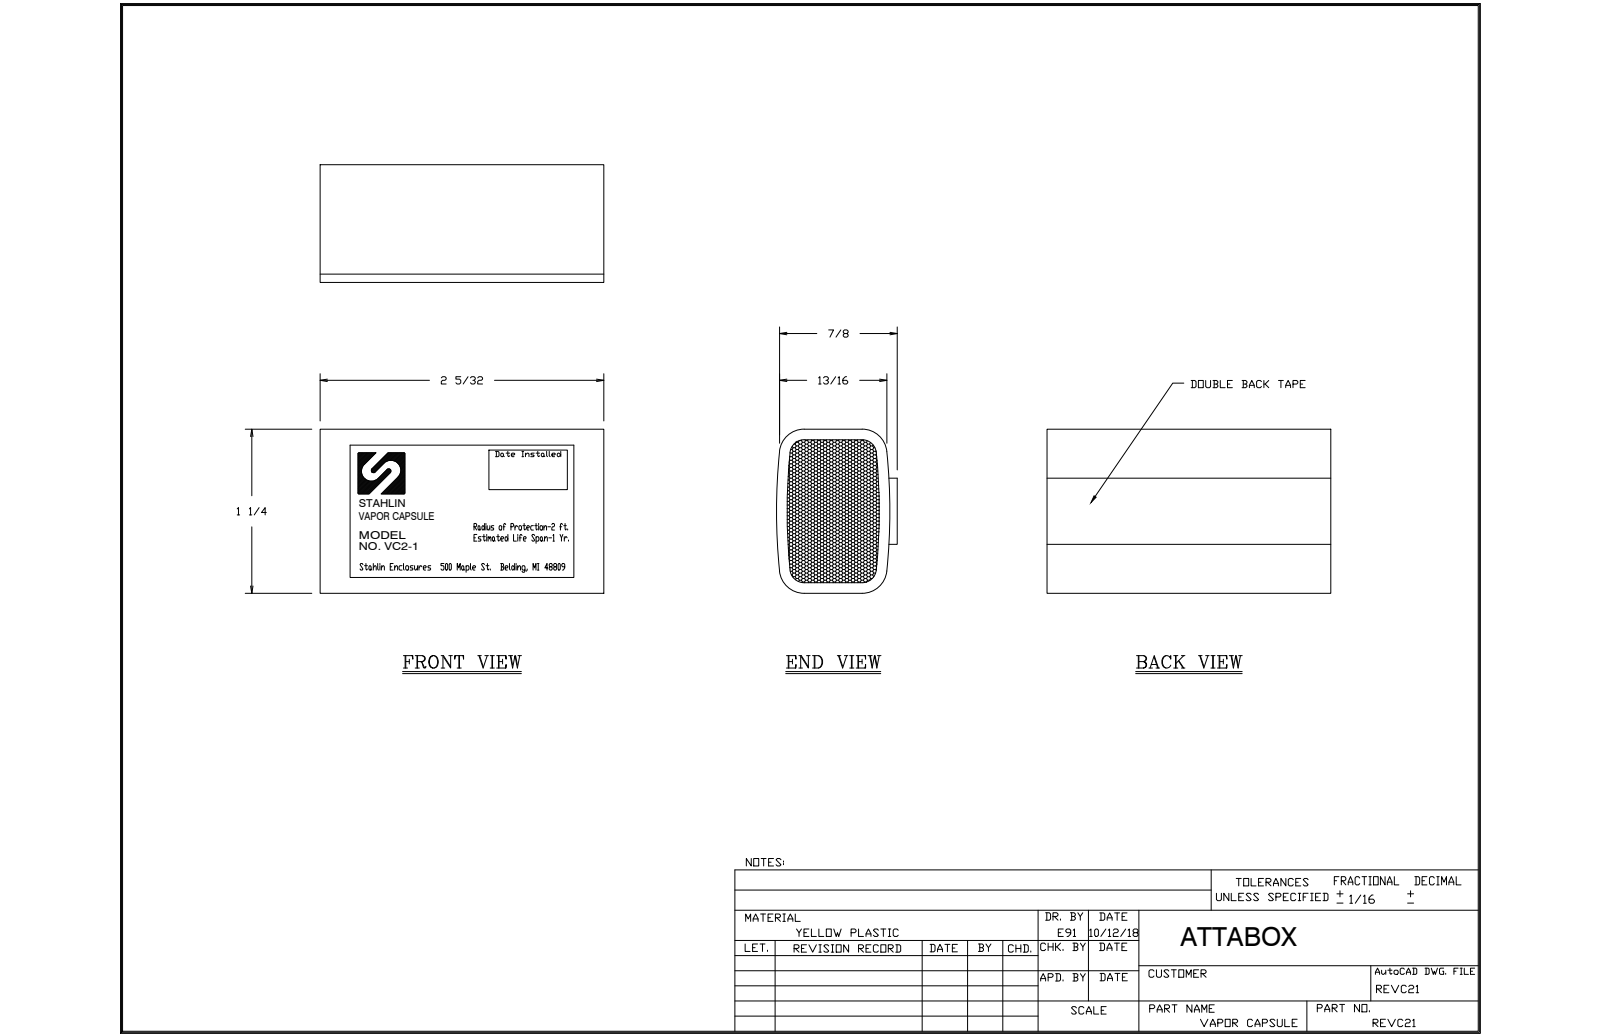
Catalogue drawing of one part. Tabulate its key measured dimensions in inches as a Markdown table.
| quantity | value |
| --- | --- |
| part name | REVC21 |
| STEP written by | SolidWorks 2018 (AUTOMOTIVE_DESIGN) |
| units | inches |
| bodies | 2 solids, 28 faces (10 planar, 18 cylindrical, 0 other) |
| overall size | 2.146 × 1.228 × 0.874 |
| volume | 2.167 in³ |
| surface area | 23.89 in² |
| partial cylindrical surfaces (radius × count) | 0.109 × 4, 0.109 × 4, 0.2 × 4, 4.12 × 2, 4.122 × 2, 4.211 × 2 |
| main face-to-face distances | 1.046, 0.091, 1.137, 2.146, 1.228 |
